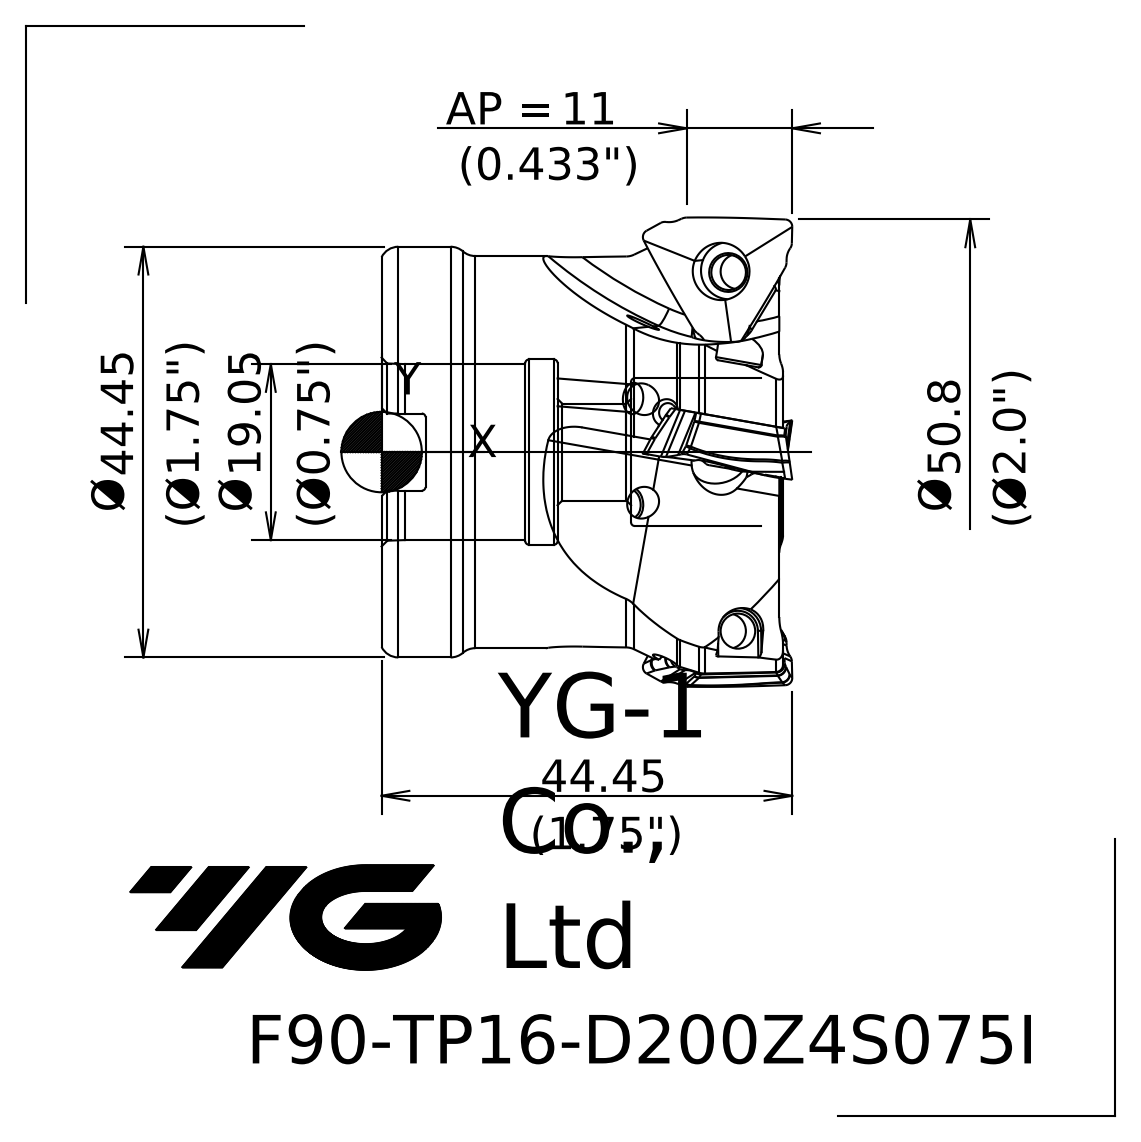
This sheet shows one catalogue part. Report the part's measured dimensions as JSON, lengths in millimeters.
{"part_name": "10224A3C590Cnhjc", "step_written_by": "SIEMENS PLM Software NX 10.0 (AP203_CONFIGURATION_CONTROLLED_3D_DESIGN_OF_MECHANICAL_PARTS_AND_ASSEMBLIES_MIM_LF)", "units": "millimeters", "bodies": {"solids": 1, "faces": 71, "planar": 17, "cylindrical": 10, "other": 44}, "overall_size": [50.89, 50.89, 44.45], "volume_mm3": 56970, "surface_area_mm2": 17670, "round_holes": [[10.5, 1], [16, 1], [19.05, 1], [20.05, 1]], "round_bosses_or_shafts": [[44.45, 1], [42.45, 1]], "partial_cylinders_radius": [[0.4, 2]], "face_to_face_distances": [43.05, 38.3, 4.75, 24, 14.3, 19.05, 8.35, 16.05, 7.95, 22.25]}
